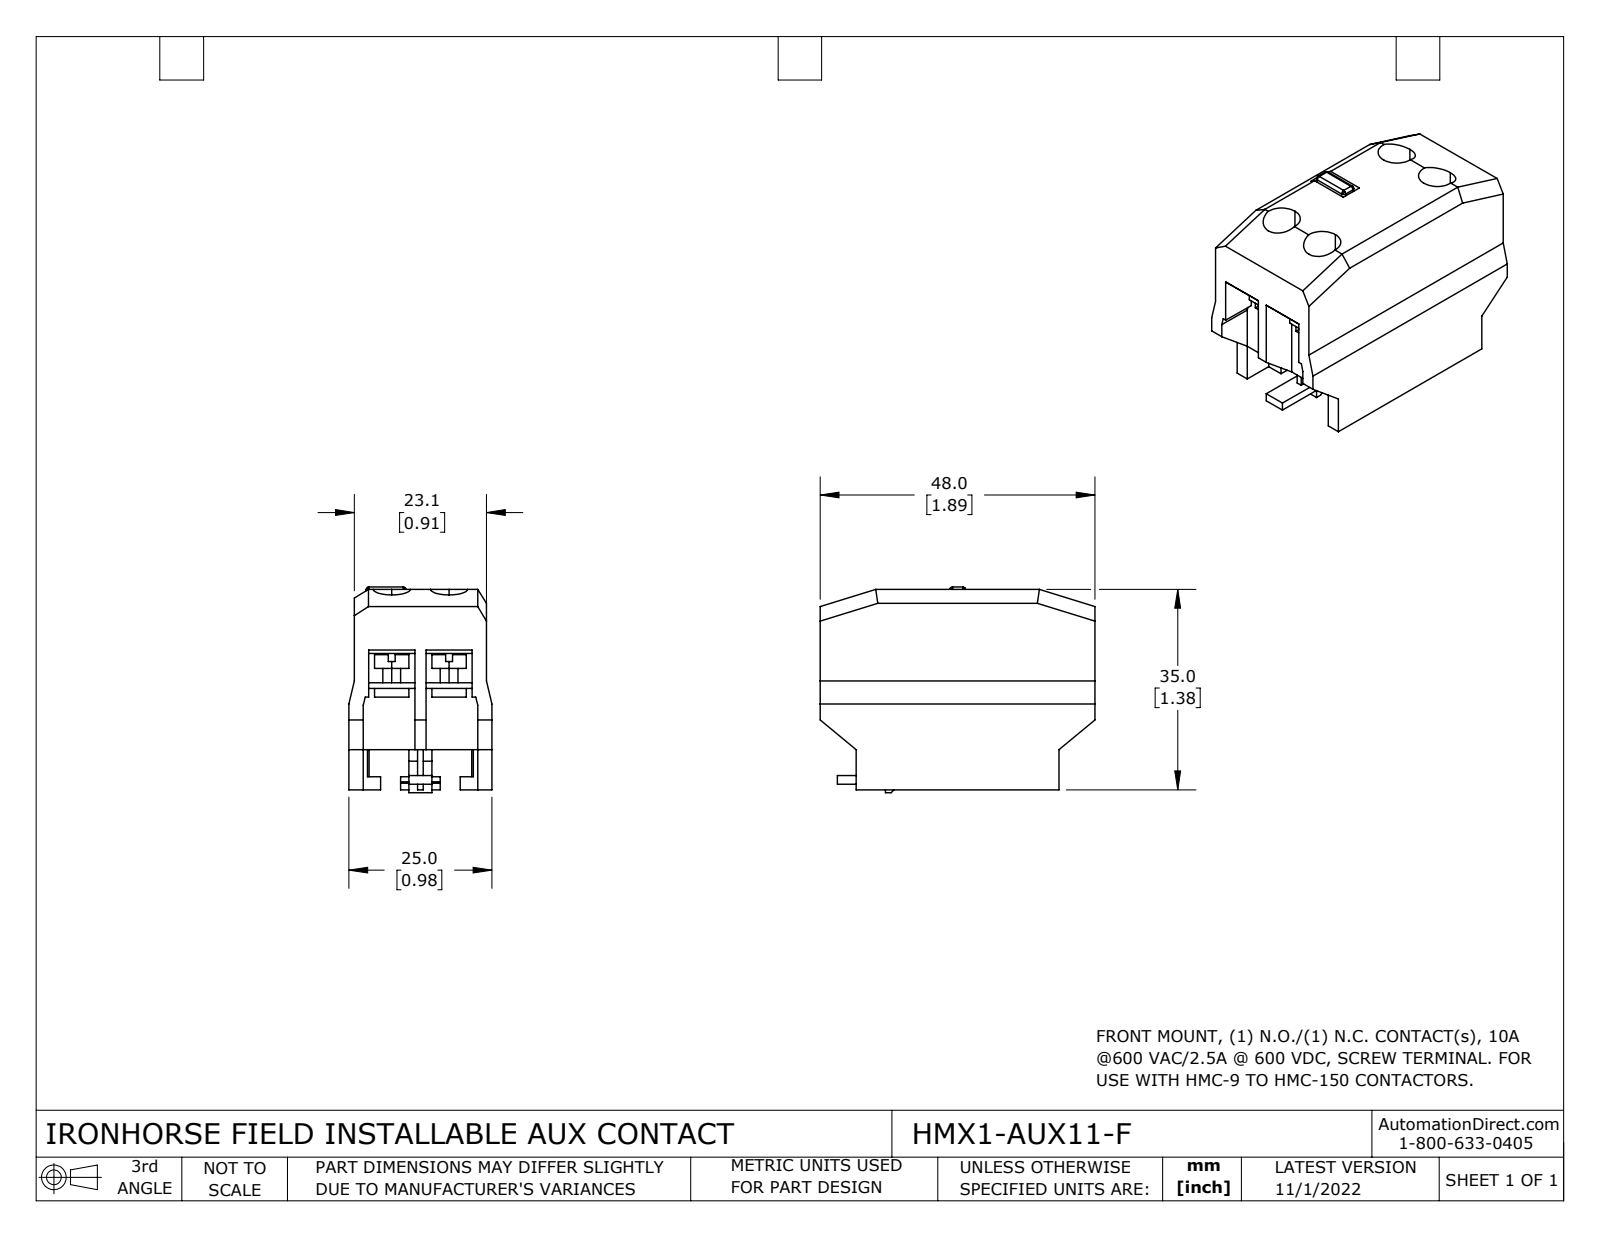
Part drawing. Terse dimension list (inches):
name: HMX1-AUX11-F
written by: SolidWorks 2021 (CONFIG_CONTROL_DESIGN)
unit: in
bodies: 6 solids, 333 faces (287 planar, 38 cylindrical, 8 other)
size: 1.89 × 1.413 × 0.984
volume: 1.442 in³; area: 19.59 in²
holes: 4× ⌀0.256
bosses: 4× ⌀0.236, 4× ⌀0.122
rounds: 12× R0.02, 1× R0.098, 1× R0.157
face distances: 0.038, 0.098, 0.946, 0.848, 0.492, 0.454, 0.53, 0.416, 0.394, 0.059
hole spacings: 0.394, 1.118, 1.185
